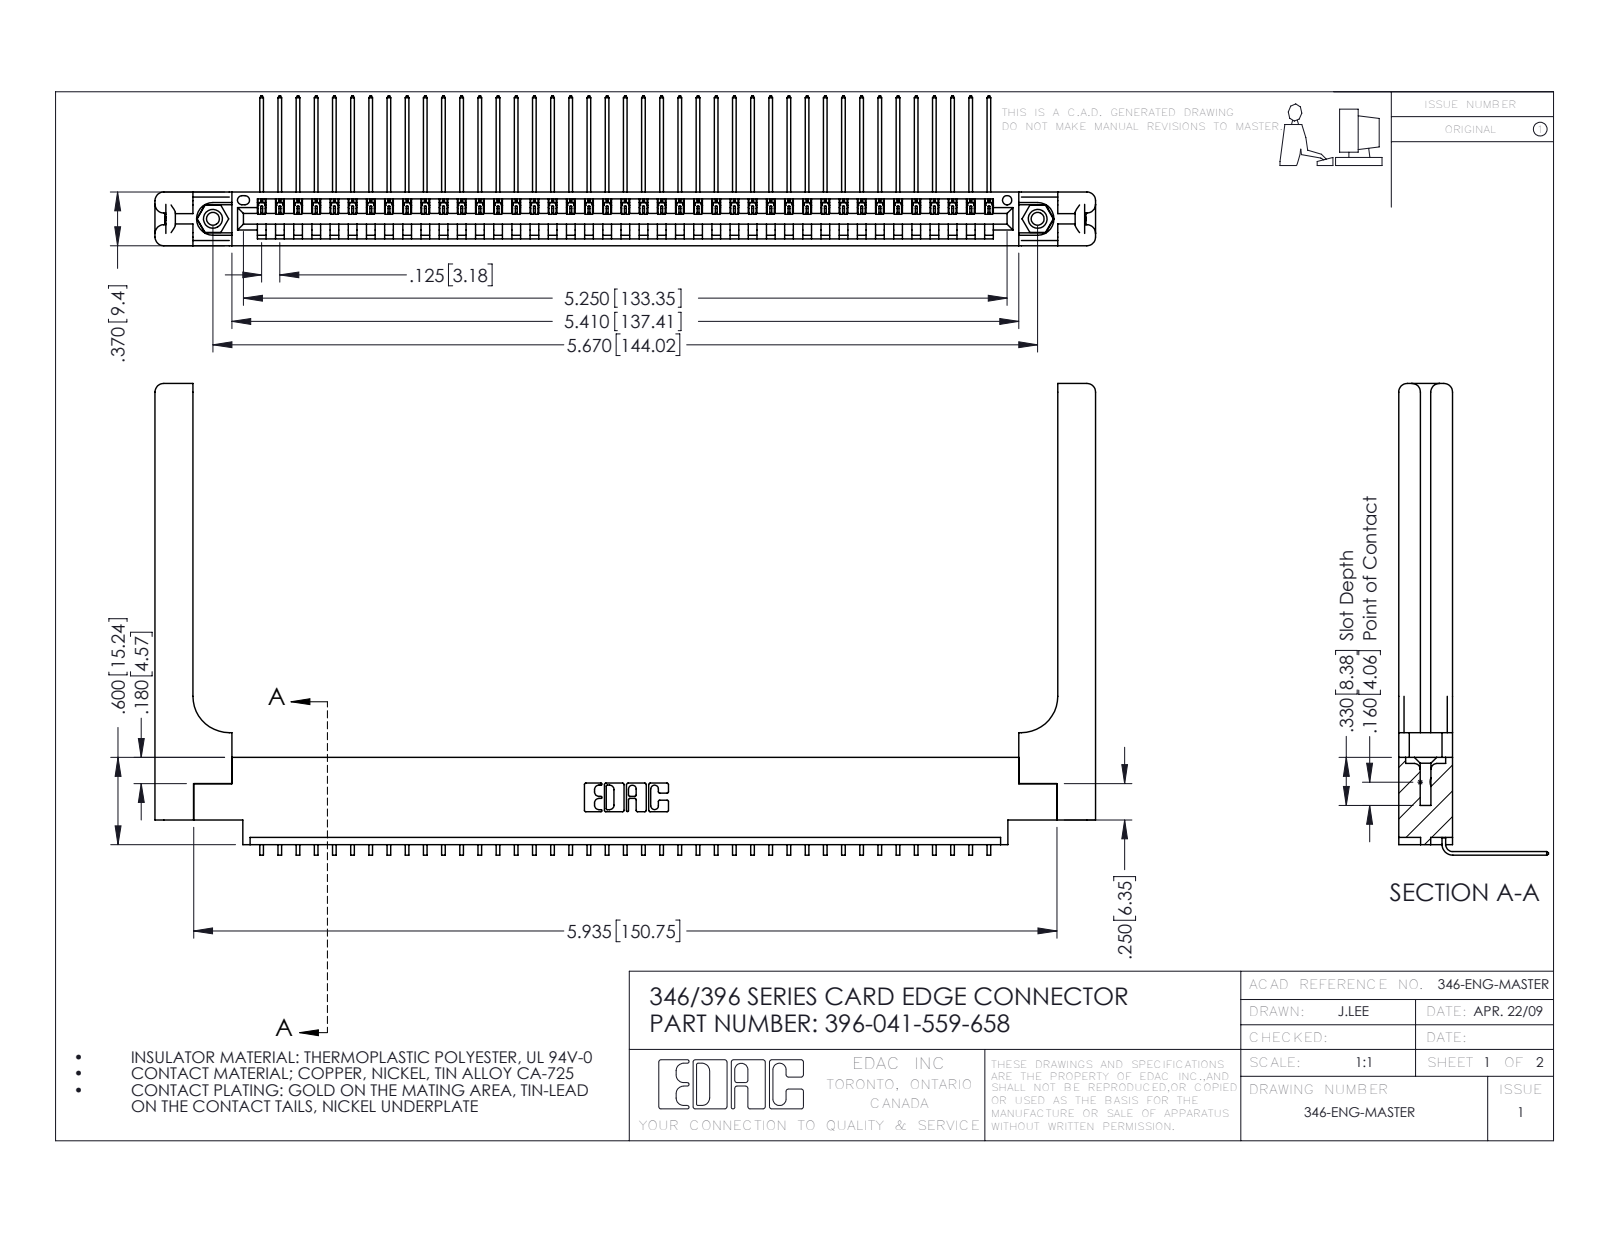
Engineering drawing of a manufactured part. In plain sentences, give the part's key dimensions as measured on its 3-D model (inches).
The part is named "345-292-001_558 559 Tail - 1; 346 Part_0.170 Offset - 0.156 Dia-TH; 396-041-559-658; 346-220-058_345-220-058 (+1 more)". Its 3-D file was written by "SolidWorks 2016 (CONFIG_CONTROL_DESIGN)". It is 46 solids with 2842 faces: 1950 planar, 832 cylindrical and 60 other. Overall it measures 6.466 by 3.243 by 1.03 inches. Its volume is 1.417 cubic inches and its surface area 39.92 square inches. Round holes: 2 of diameter 0.089, 2 of diameter 0.125, 2 of diameter 0.156, 1 of diameter 0.064. Round bosses or shafts: 2 of diameter 0.155. Partial cylindrical surfaces (rounded edges, fillets, slot ends): 82 of radius 0.006, 22 of radius 0.01, 16 of radius 0.06, 6 of radius 0.007, 6 of radius 0.031, 3 of radius 0.026, 2 of radius 0.03, 2 of radius 0.031. The main face-to-face distances are 0.37, 0.048, 0.322, 0.072, 0.148, 0.15, 0.025, 0.25, 0.298, 0.222. The hole center spacings are 0.246, 5.461, 5.67.
